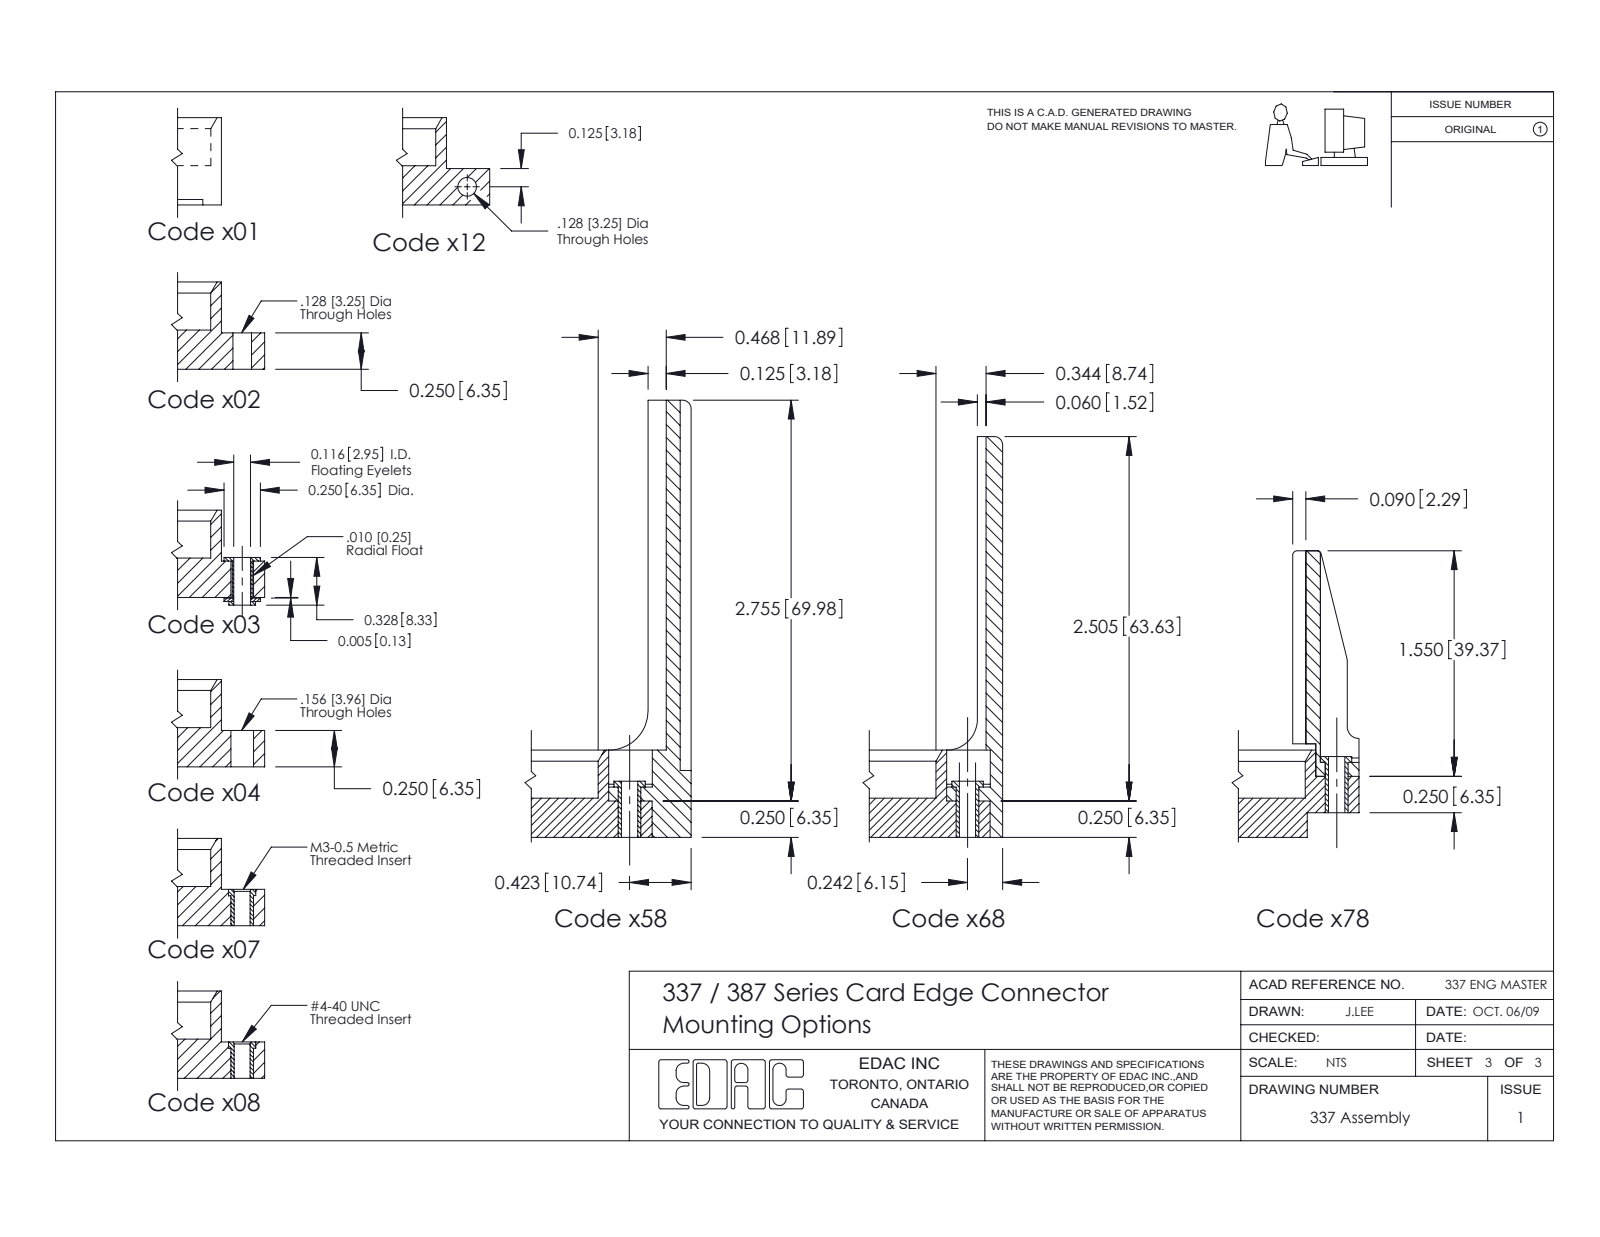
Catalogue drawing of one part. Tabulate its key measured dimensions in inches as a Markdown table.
| quantity | value |
| --- | --- |
| part name | 337-008-521-604; 345-292-001_345-293-121; 337 Part_0.170 Offset - 0.156 Dia-TH |
| STEP written by | SolidWorks 2016 (CONFIG_CONTROL_DESIGN) |
| units | inches |
| bodies | 9 solids, 614 faces (442 planar, 172 cylindrical, 0 other) |
| overall size | 2.154 × 0.75 × 0.37 |
| volume | 0.307 in³ |
| surface area | 7.451 in² |
| round holes (diameter × count) | 0.156 × 2 |
| partial cylindrical surfaces (radius × count) | 0.01 × 22, 0.006 × 16, 0.01 × 16, 0.007 × 6, 0.031 × 6, 0.026 × 3, 0.014 × 1, 0.022 × 1 |
| main face-to-face distances | 0.37, 0.072, 0.298, 0.149, 0.156, 0.098, 0.272, 0.025, 0.2, 0.072 |
| hole center spacings | 1.844 |
